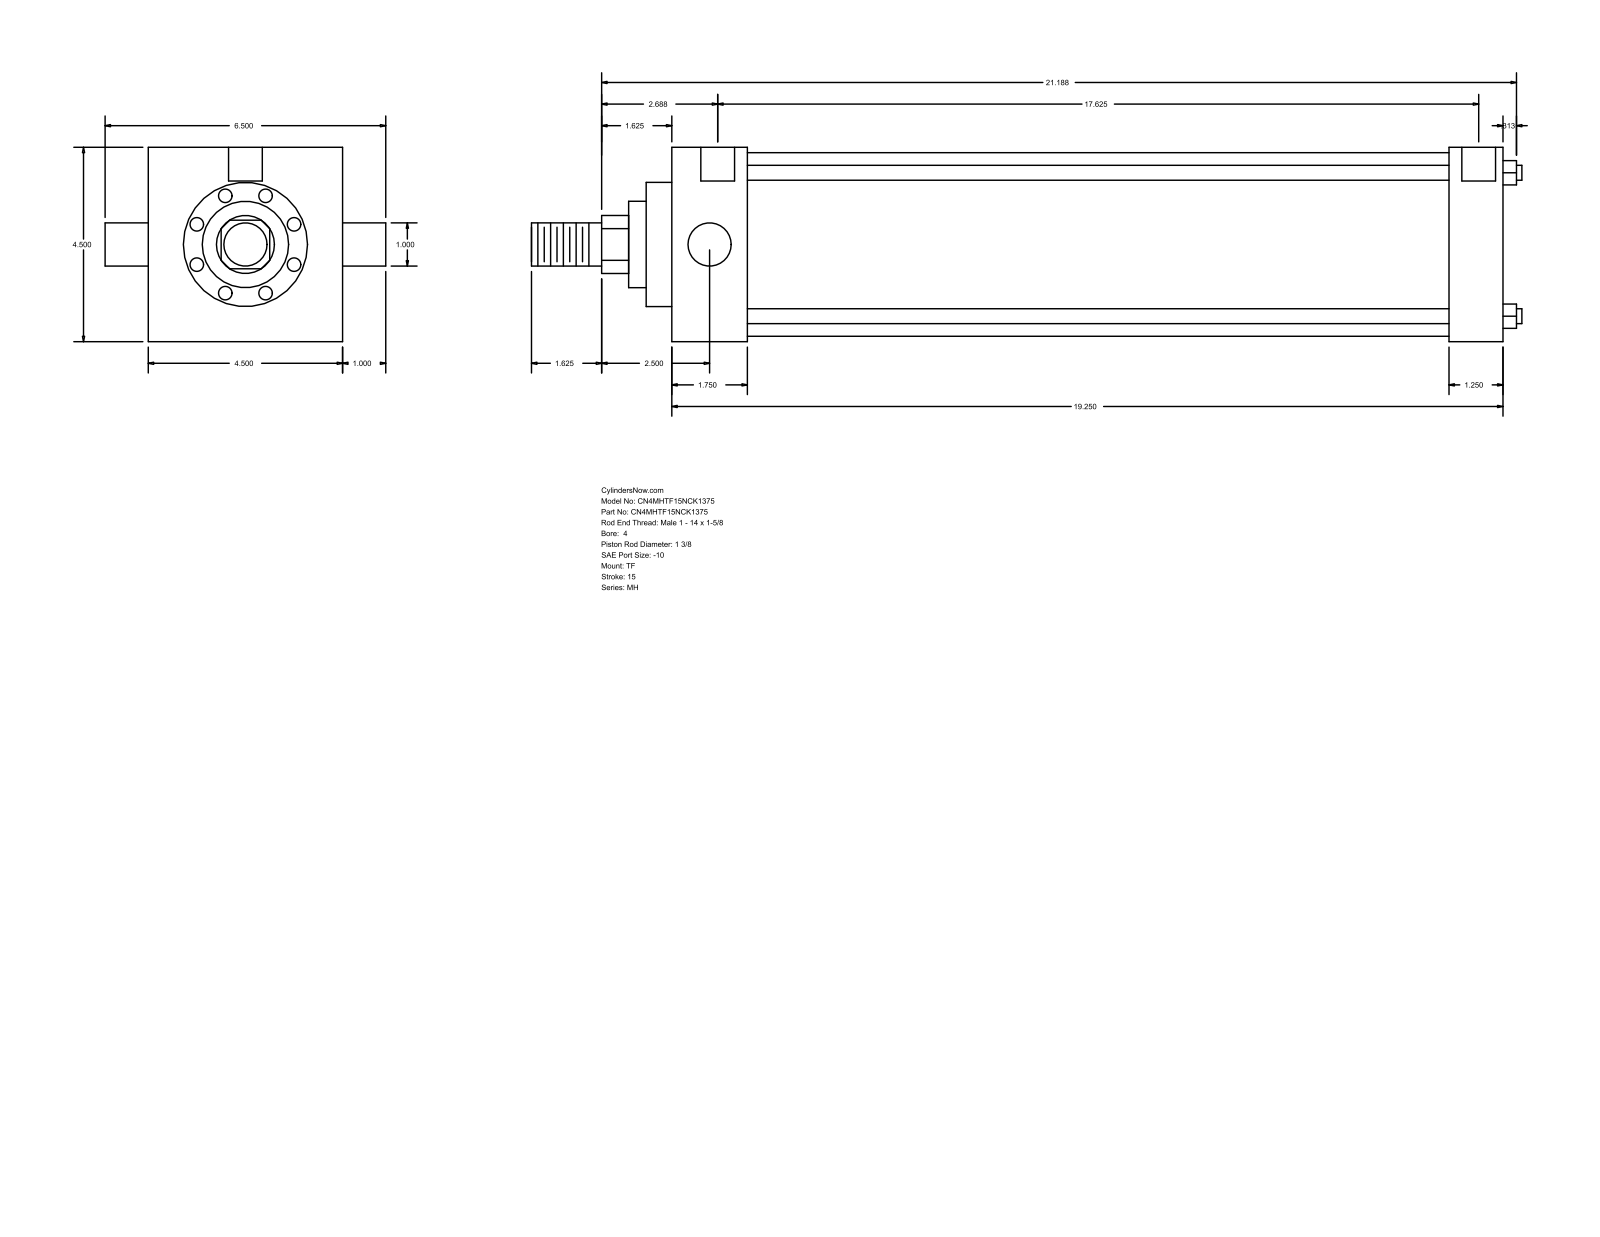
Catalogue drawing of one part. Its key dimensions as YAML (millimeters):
part_name: "MH_TF__0400_1.375"
step_written_by: "GSSL Pune (CONFIG_CONTROL_DESIGN)"
units: millimeters
bodies: {solids: 0, faces: 86, planar: 61, cylindrical: 25, other: 0}
overall_size: [582.61, 165.1, 114.3]
round_holes:
  - {diameter: 8.73, count: 3}
  - {diameter: 19.84, count: 2}
round_bosses_or_shafts:
  - {diameter: 8.76, count: 4}
  - {diameter: 25.4, count: 2}
  - {diameter: 107.95, count: 1}
  - {diameter: 73.03, count: 1}
  - {diameter: 50.8, count: 1}
  - {diameter: 34.92, count: 1}
partial_cylinders:
  - {radius: 17.06, count: 1}
face_to_face_distances: [114.3, 488.96, 44.45, 444.51, 457.21, 412.76, 31.75, 15.08, 59.53, 472.29]
hole_center_spacings: [1.58, 1.59, 447.68, 449.26, 449.27, 450.85]
